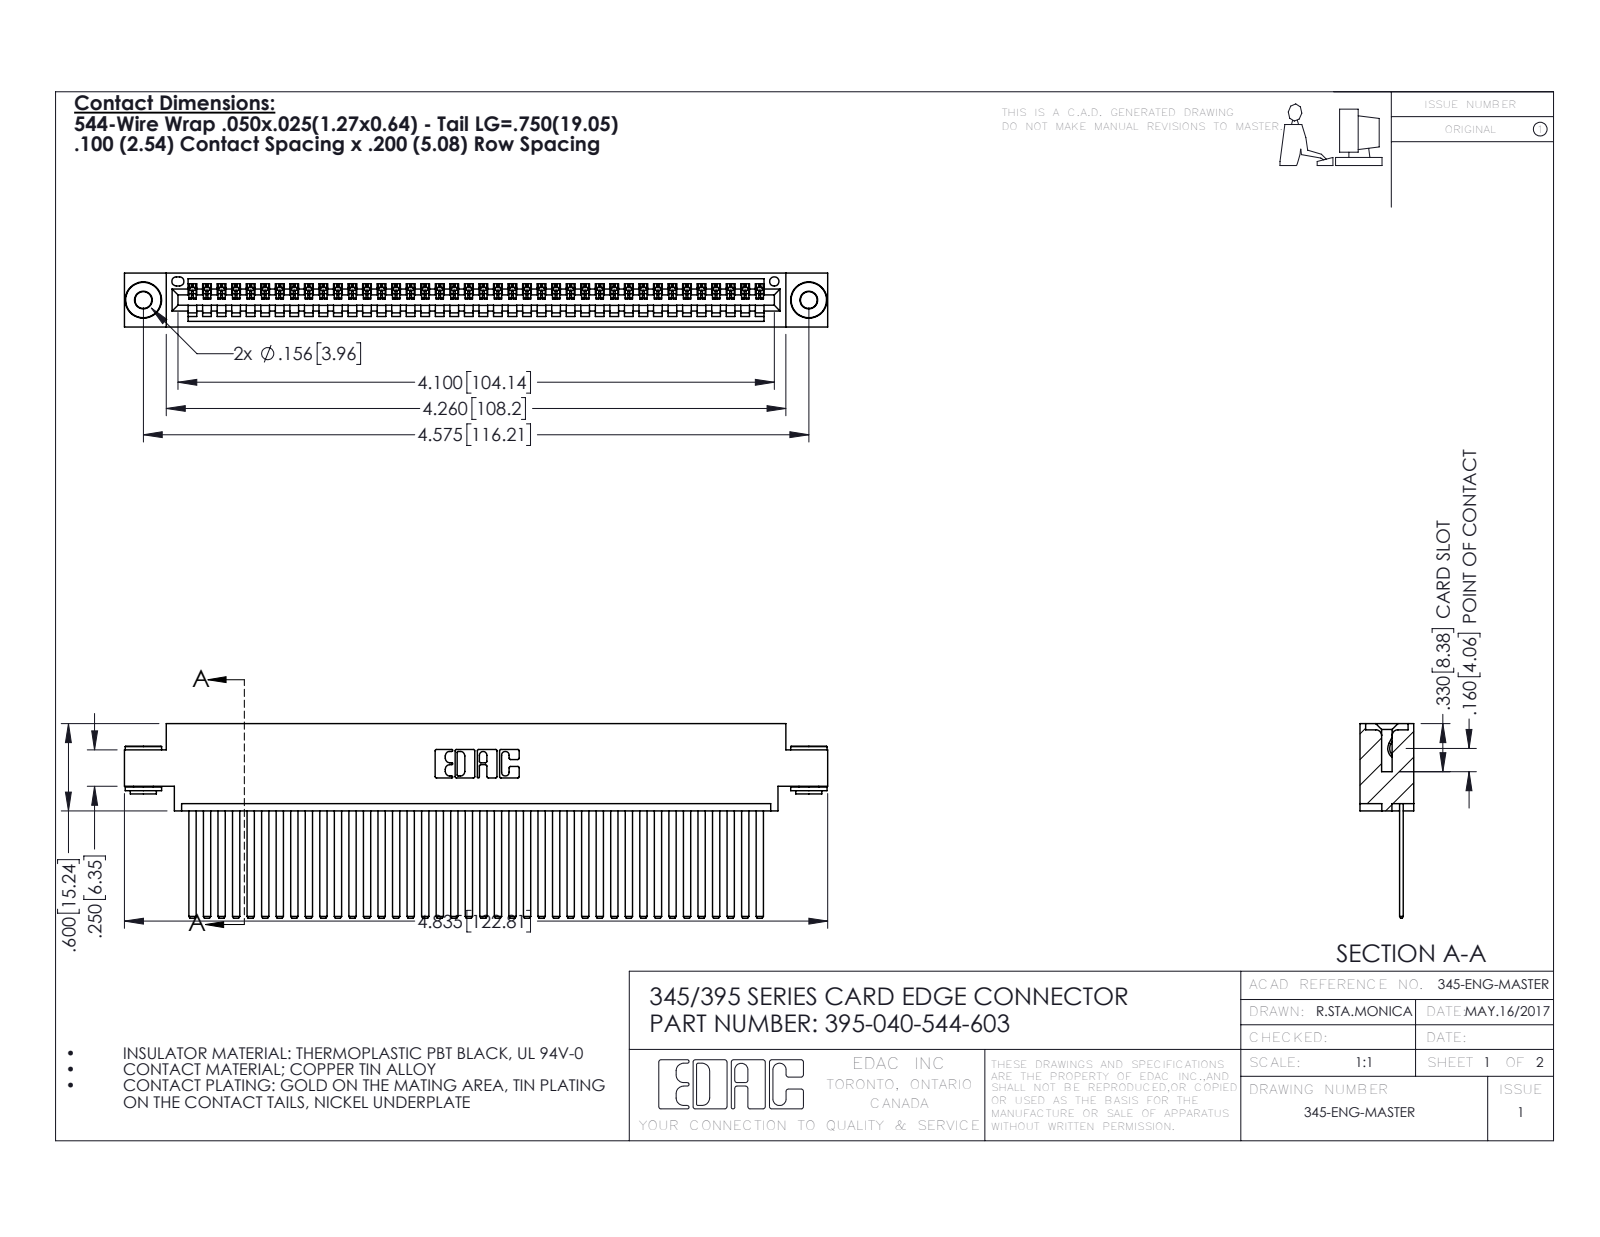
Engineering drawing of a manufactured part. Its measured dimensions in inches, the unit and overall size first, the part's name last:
Units: inches
Overall size (bounding box): 4.835 × 1.337 × 0.37
Round holes (diameter × count): ⌀0.116 ×2, ⌀0.156 ×2, ⌀0.064 ×1
Round bosses / shafts (diameter × count): ⌀0.25 ×2, ⌀0.18 ×2, ⌀0.136 ×2
Partial cylindrical surfaces — rounded edges, fillets, slot ends (radius × count): R0.006 ×80, R0.01 ×22, R0.007 ×6, R0.031 ×6, R0.026 ×3, R0.031 ×2, R0.04 ×2, R0.014 ×1
Main face-to-face distances: 0.072, 0.298, 0.025, 0.098, 0.272, 0.37, 0.2, 0.225, 0.175, 0.149
Hole centre spacings: 0.27, 4.339, 4.575
Volume: 0.733 in³ · Surface area: 27.4 in²
Bodies: 43 solids, 2248 faces (1534 planar, 706 cylindrical, 8 other)
Part name (STEP PRODUCT): 345-292-001_345-293-144; 345 Part_0.170 Offset - 0.156 Dia-TH; 345-250-002_345-250-002-102; 395-040-544-603
STEP written by: SolidWorks 2016 (CONFIG_CONTROL_DESIGN)
